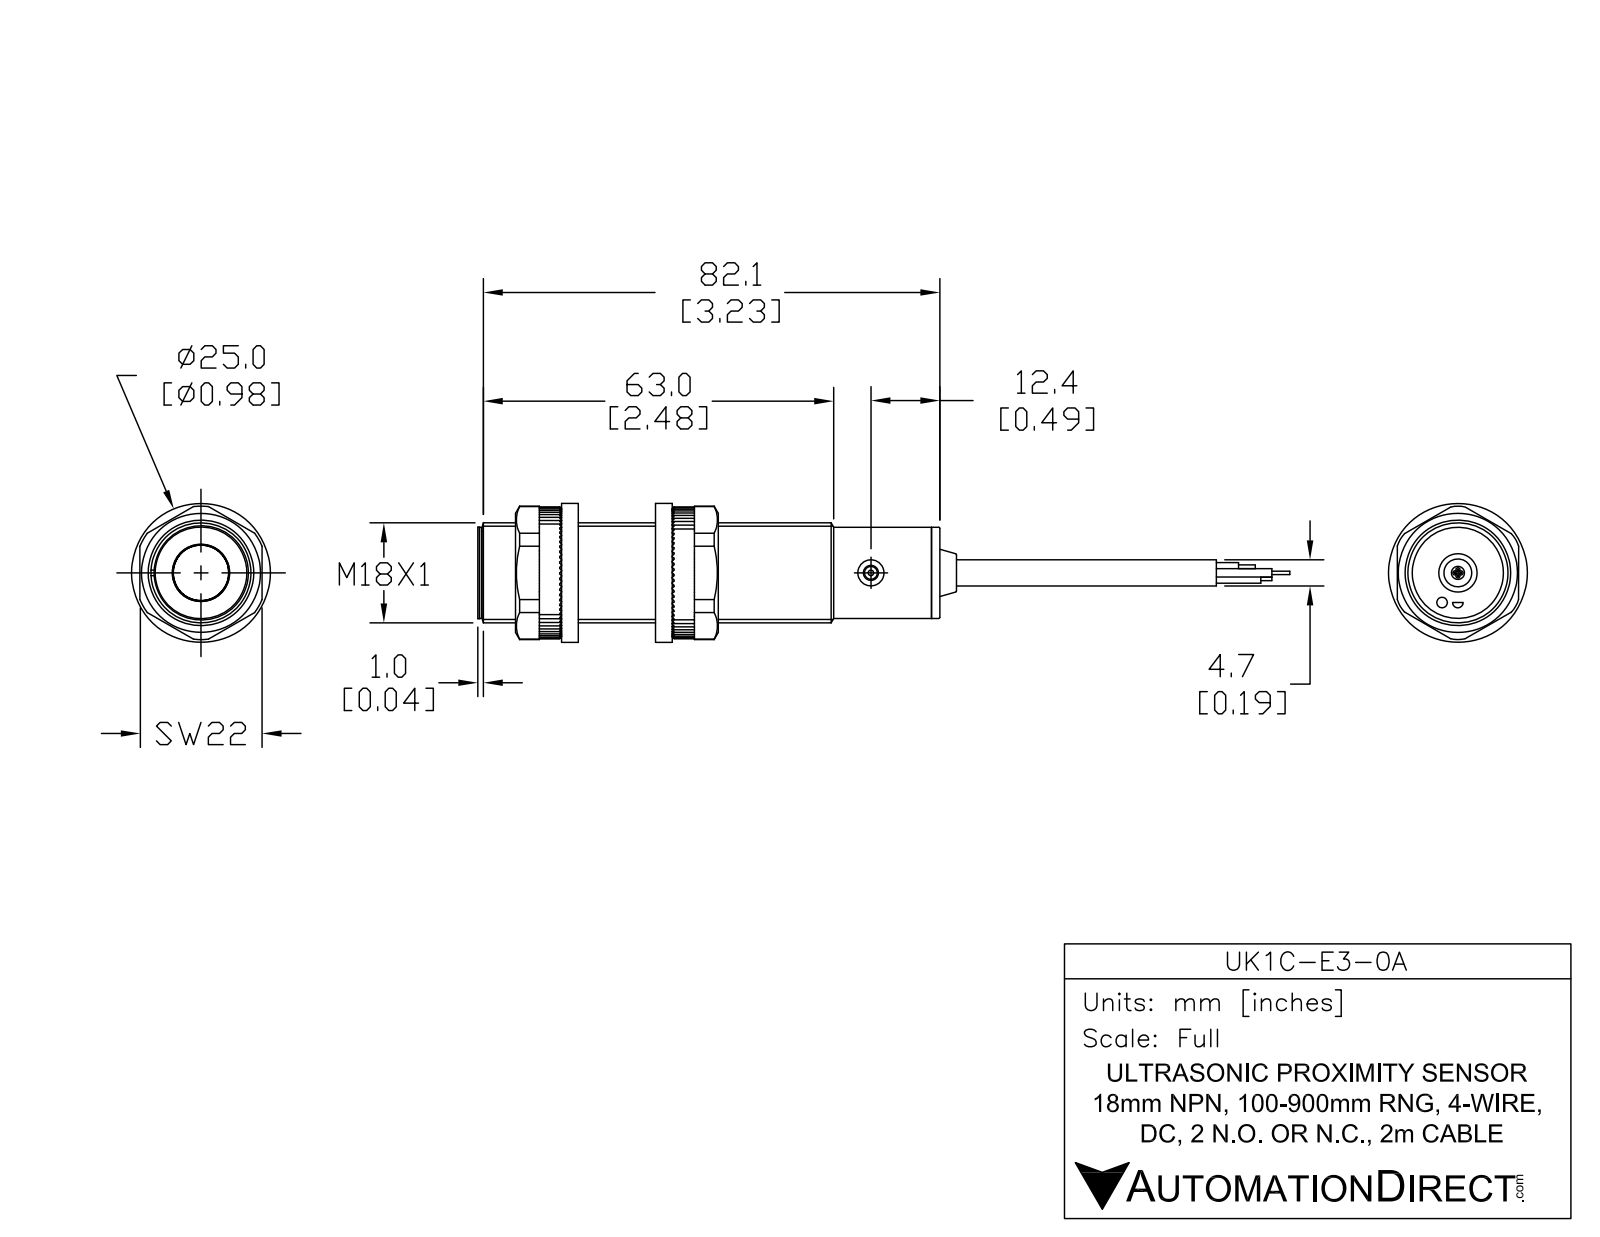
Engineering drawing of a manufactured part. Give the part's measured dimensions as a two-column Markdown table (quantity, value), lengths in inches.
| quantity | value |
| --- | --- |
| part name | UK1C-E3-0A |
| STEP written by | SolidWorks 2017 (AUTOMOTIVE_DESIGN) |
| units | inches |
| bodies | 6 solids, 55 faces (17 planar, 24 cylindrical, 14 other) |
| overall size | 4.832 × 0.709 × 0.709 |
| volume | 1.285 in³ |
| surface area | 10.69 in² |
| round holes (diameter × count) | 0.185 × 2, 0.106 × 1 |
| round bosses / shafts (diameter × count) | 0.709 × 1, 0.646 × 1, 0.622 × 1, 0.374 × 1, 0.189 × 1, 0.091 × 1 |
| main face-to-face distances | 3.193, 3.252, 0.059, 0.039, 3.232, 3.291, 0.041, 3.234, 3.293, 3.257 |
